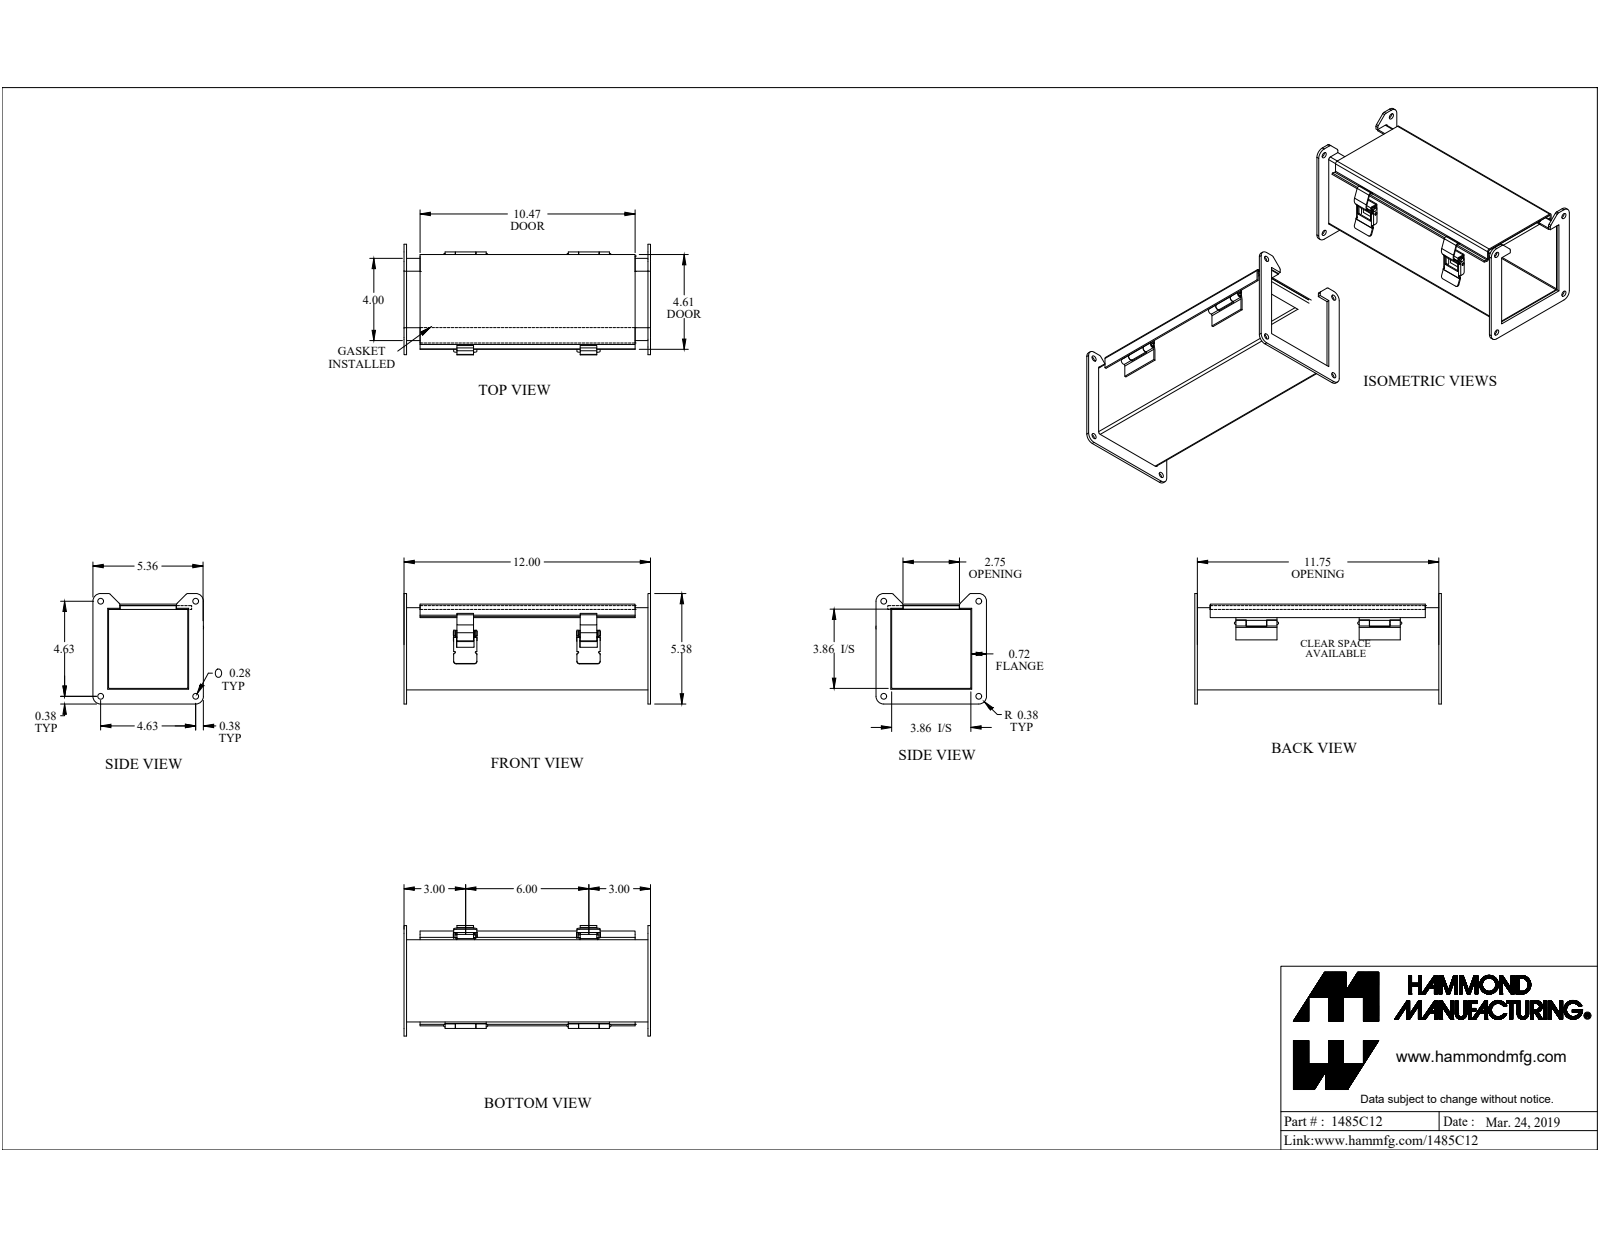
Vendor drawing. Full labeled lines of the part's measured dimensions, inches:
Part name (STEP PRODUCT): 1485C12
STEP written by: SolidWorks 2019 (CONFIG_CONTROL_DESIGN)
Units: inches
Bodies: 20 solids, 410 faces (250 planar, 156 cylindrical, 4 other)
Overall size (bounding box): 12 × 5.383 × 5.375
Volume: 22.69 in³ · Surface area: 569.5 in²
Round holes (diameter × count): ⌀0.281 ×4, ⌀0.125 ×1, ⌀0.13 ×1, ⌀0.164 ×1
Round bosses / shafts (diameter × count): ⌀0.187 ×2, ⌀0.275 ×1, ⌀0.156 ×1, ⌀0.125 ×1
Partial cylindrical surfaces — rounded edges, fillets, slot ends (radius × count): R0.016 ×13, R0.125 ×9, R0.036 ×7, R0.108 ×7, R0.035 ×5, R0.039 ×5, R0.076 ×5, R0.015 ×4
Main face-to-face distances: 0.072, 3.928, 4.1, 4, 3.856, 4.028, 4.172, 0.172, 0.125, 11.875
Hole centre spacings: 4.625, 6.541, 0.285, 1.075, 1.57, 1.849, 2.785, 3.057
